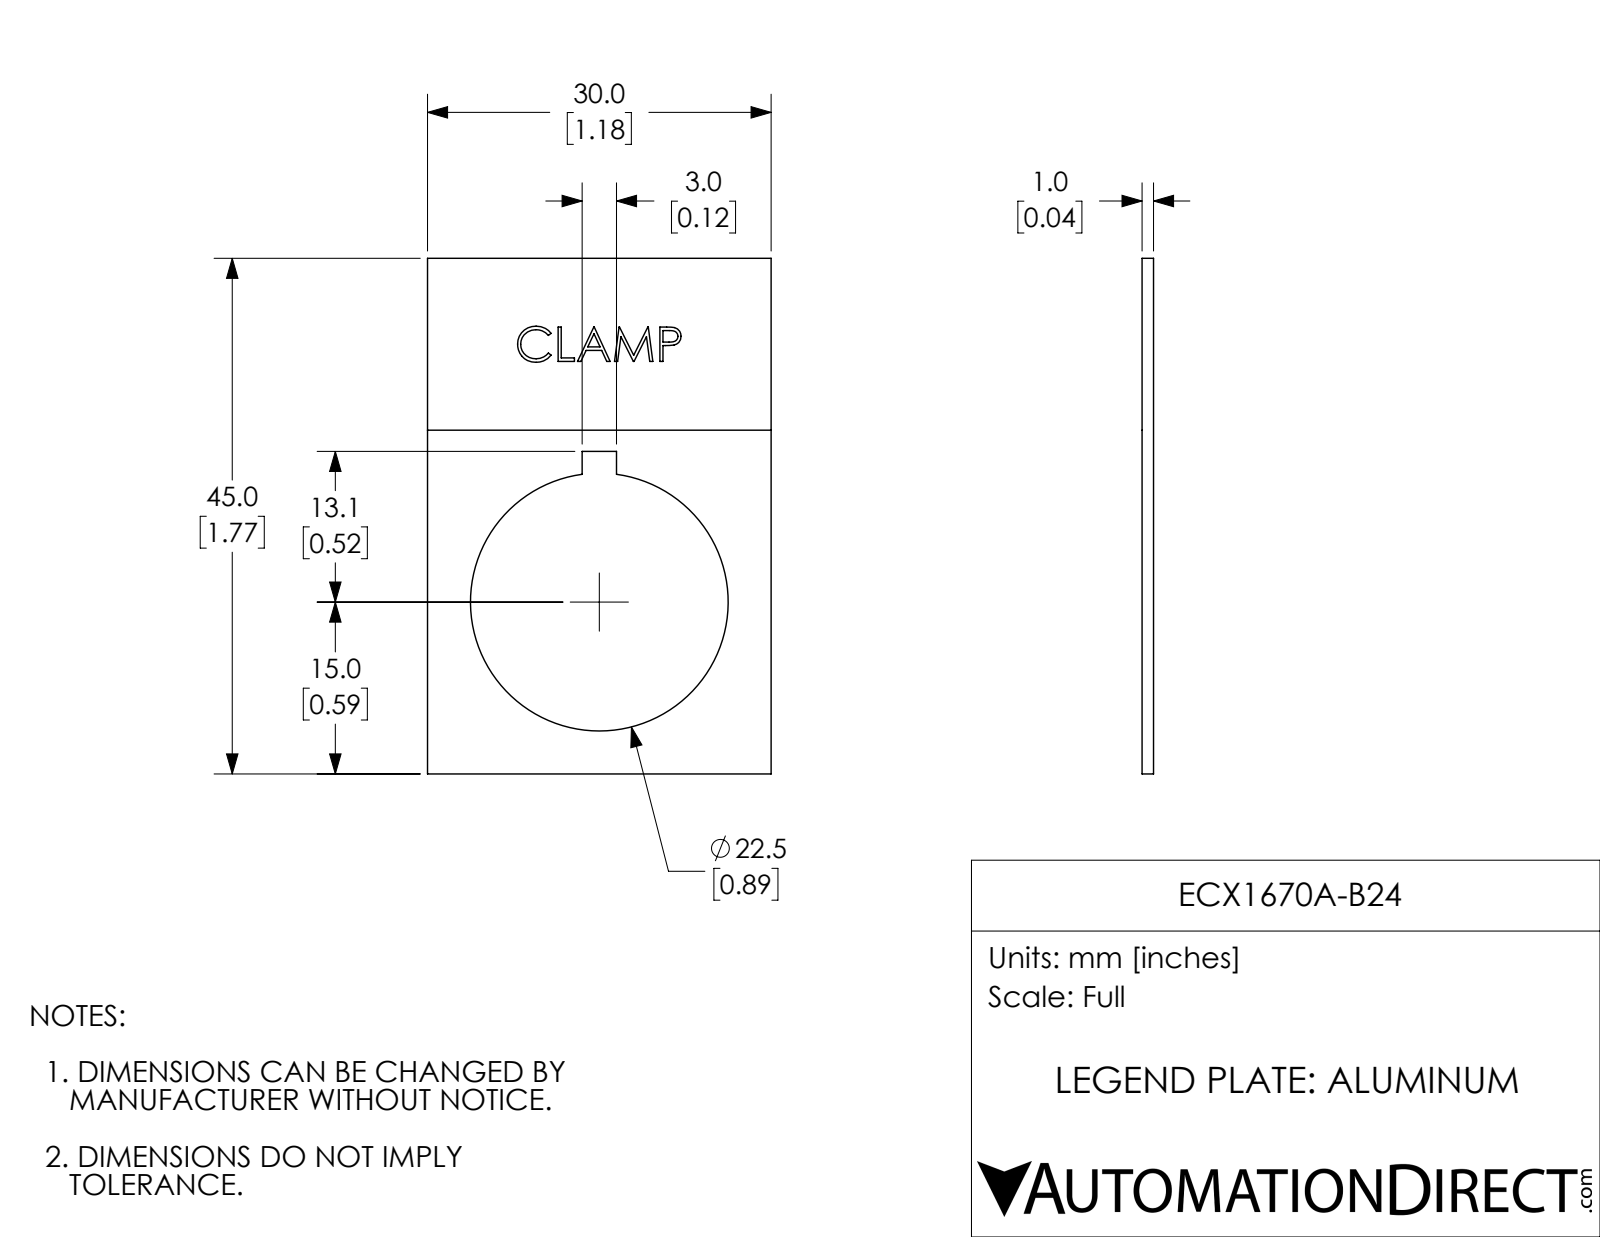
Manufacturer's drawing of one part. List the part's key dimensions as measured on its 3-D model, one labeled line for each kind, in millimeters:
Part name (STEP PRODUCT): ECX1670A-B24
STEP written by: SolidWorks 2017 (AUTOMOTIVE_DESIGN)
Units: millimetres
Bodies: 1 solid, 75 faces (57 planar, 3 cylindrical, 15 other)
Overall size (bounding box): 45 × 30 × 1
Volume: 950 mm³ · Surface area: 2 120 mm²
Round holes (diameter × count): ⌀22.5 ×1
Main face-to-face distances: 1, 30, 45, 1, 13.5, 16.5, 28.1, 16.8, 3, 8.9
